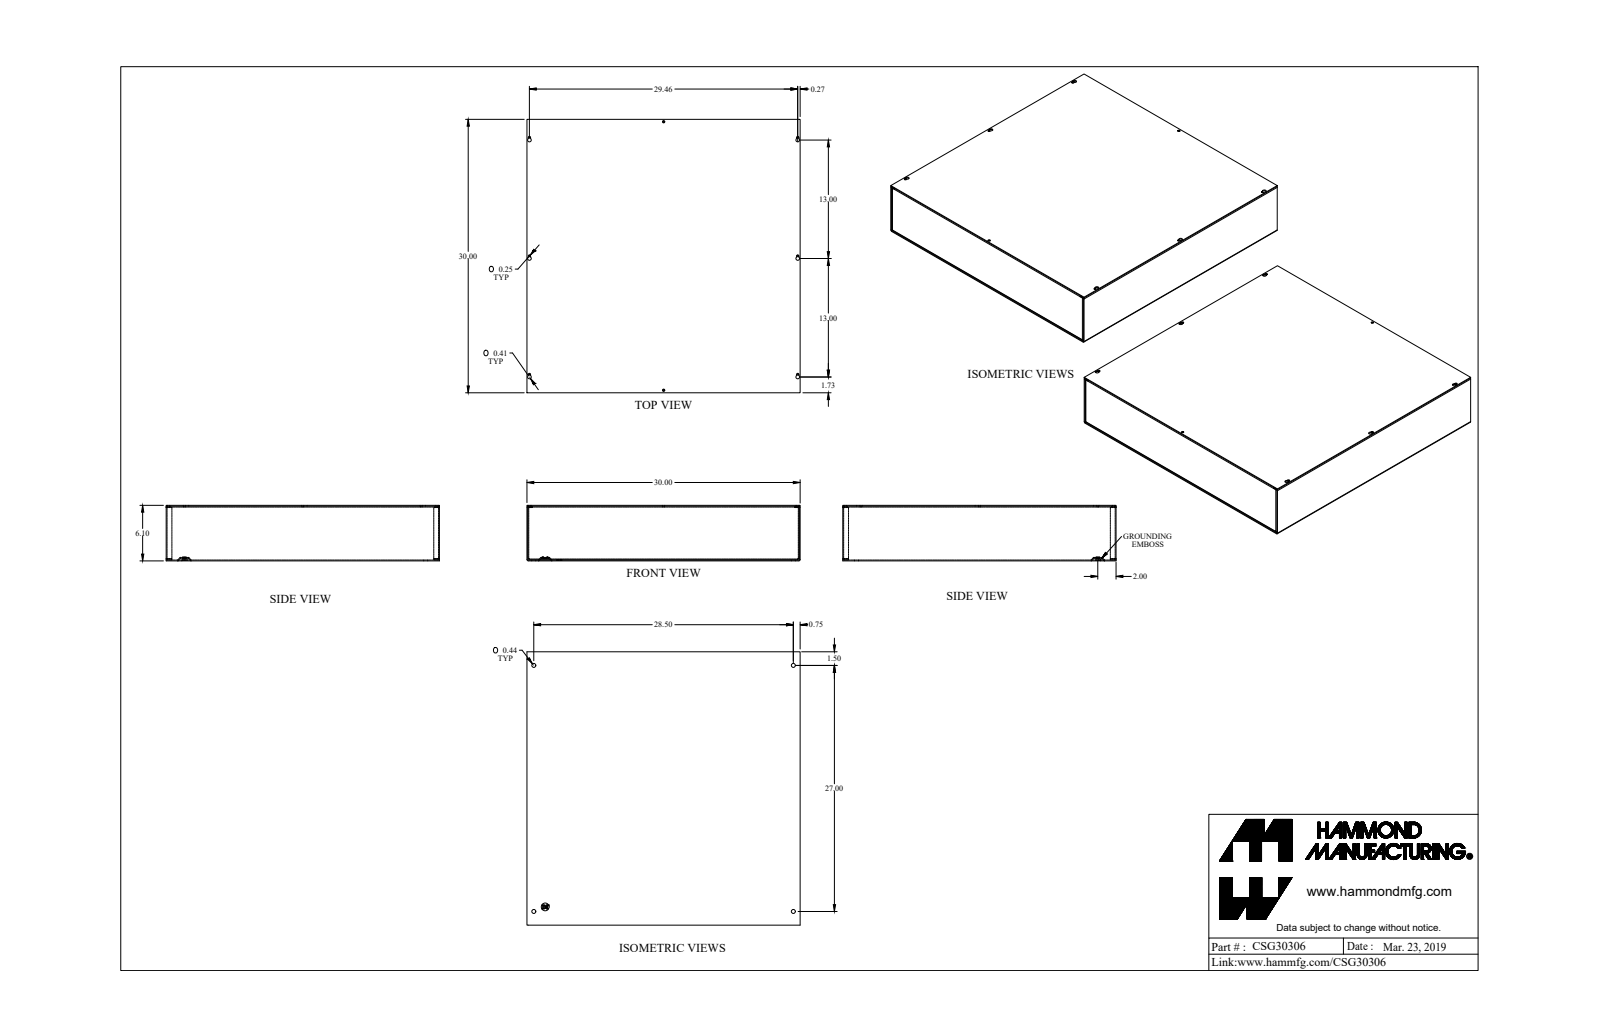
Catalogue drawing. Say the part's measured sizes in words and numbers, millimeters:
The part is named "CSG30306_Default". Its 3-D file was written by "SolidWorks 2019 (CONFIG_CONTROL_DESIGN)". It is 4 solids with 221 faces: 121 planar, 92 cylindrical and 8 other. Overall it measures 762 by 762 by 154.8 millimeters. Its volume is 4 021 000 cubic millimeters and its surface area 3 361 000 square millimeters. Round holes: 9 of diameter 4.3, 4 of diameter 11.1, 2 of diameter 6.4, 1 of diameter 12.7. Round bosses or shafts: 1 of diameter 12.5, 1 of diameter 9.1. Partial cylindrical surfaces (rounded edges, fillets, slot ends): 12 of radius 1.2, 12 of radius 3.6, 8 of radius 2.4, 6 of radius 3.2, 6 of radius 5.2. The main face-to-face distances are 2.4, 152.4, 150, 154.8, 759.6, 762, 757.2, 4.8, 147.6, 5.2. The hole center spacings are 17.6, 330.2, 343.1, 363.3, 376.7, 529.1, 673.2, 736.2.
